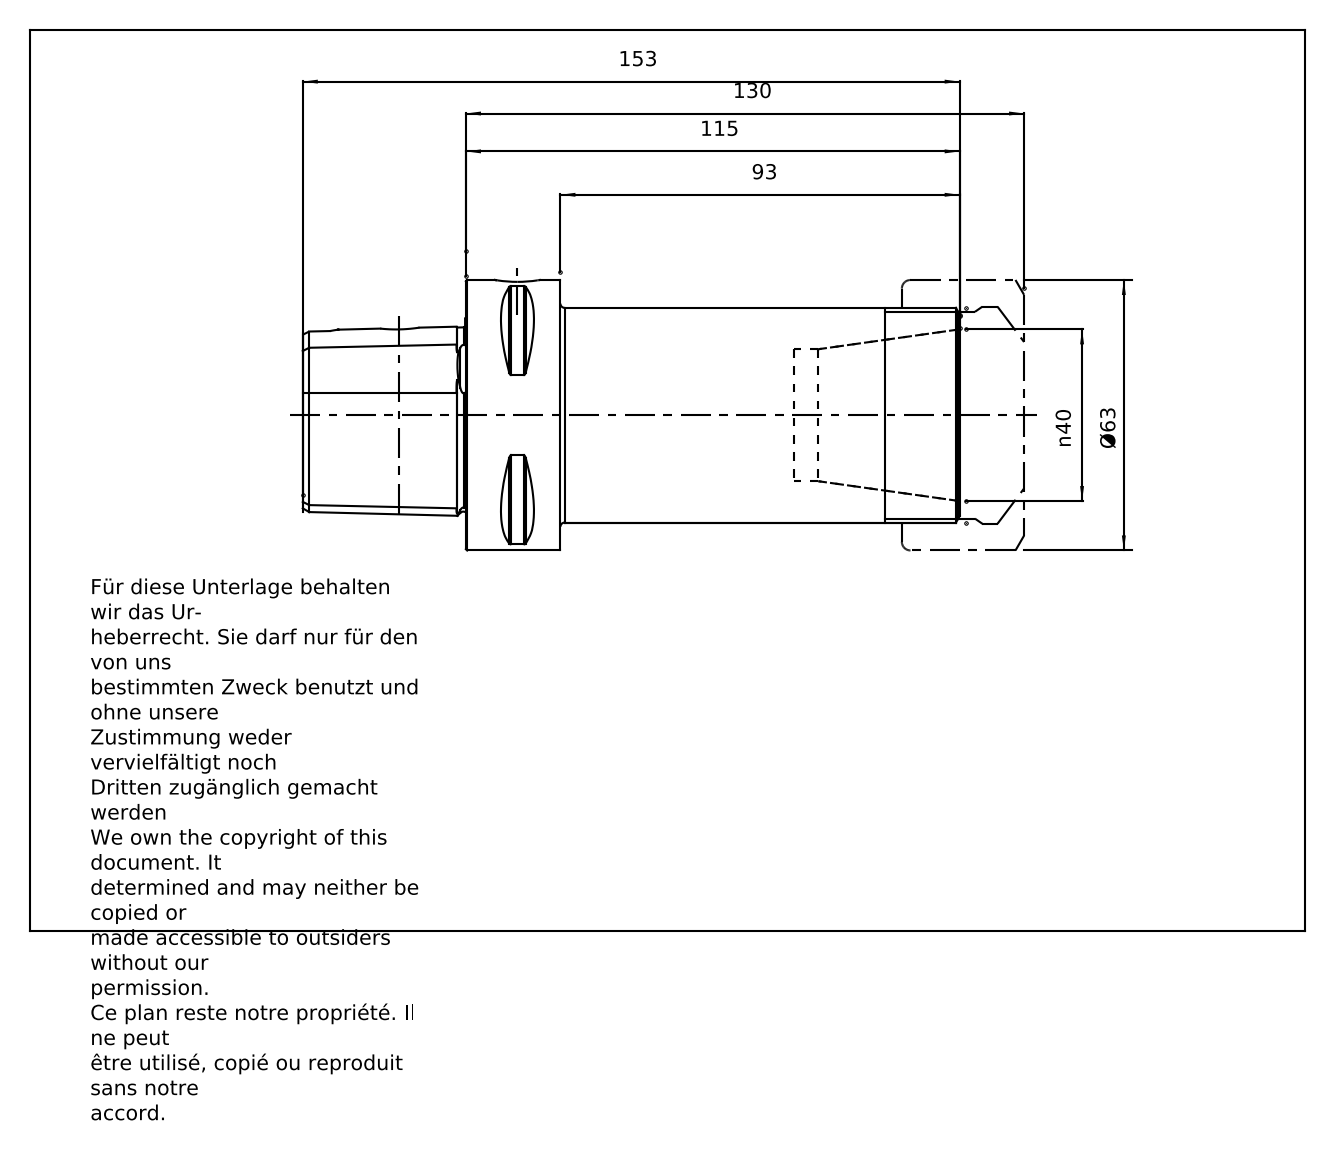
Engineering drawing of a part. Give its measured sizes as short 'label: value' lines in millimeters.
name: CC6-024-40; 83-912-40; CC6-024-40_ASM
written by: PRO/ENGINEER BY PARAMETRIC TECHNOLOGY CORPORATION, 2010430 (CONFIG_CONTROL_DESIGN)
unit: mm
bodies: 2 solids, 164 faces (51 planar, 41 cylindrical, 72 other)
size: 168 × 63 × 63
volume: 317 627 mm³; area: 50 549 mm²
holes: 1× ⌀4.25, 1× ⌀8.1, 1× ⌀10.04, 1× ⌀18, 1× ⌀28.02, 1× ⌀30.5, 1× ⌀32
bosses: 1× ⌀63, 1× ⌀50, 1× ⌀20
rounds: 8× R0.5, 6× R2.7, 1× R6
face distances: 25.5, 104.5, 130, 38, 115, 22, 82.5, 108, 77, 55
hole spacings: 27.5
